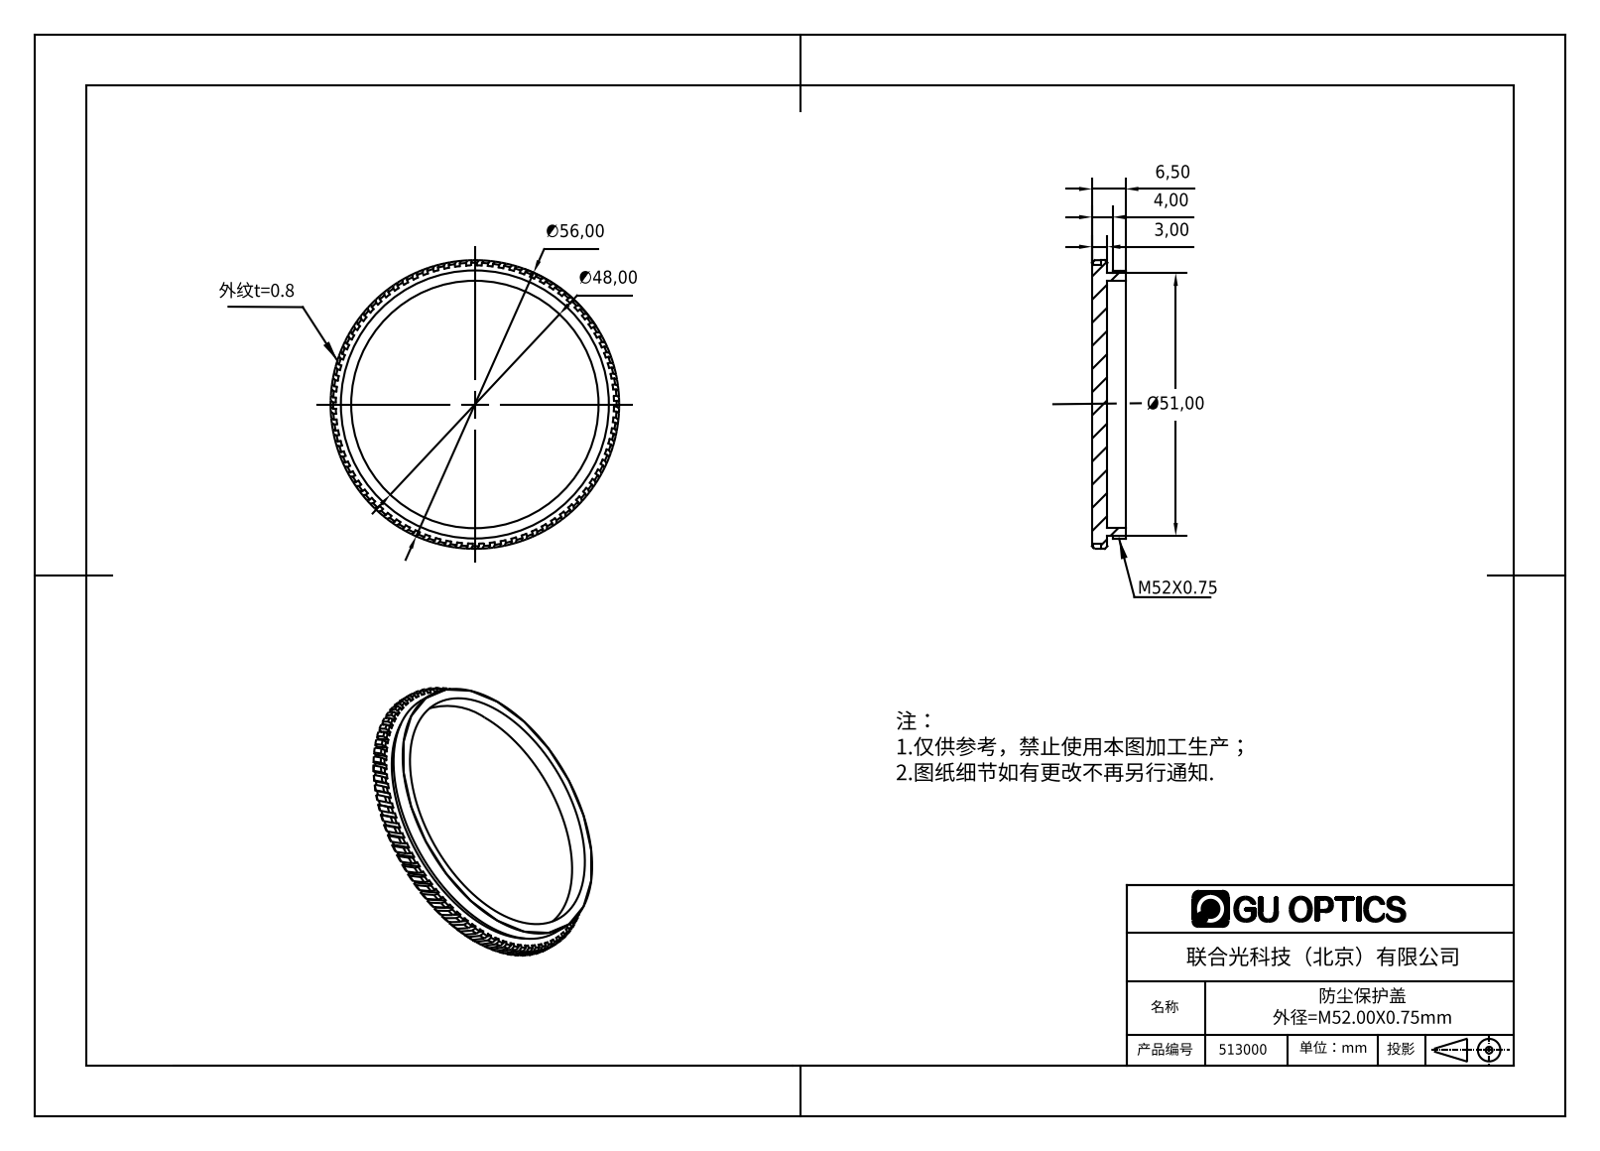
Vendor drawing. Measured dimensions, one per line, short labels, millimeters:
name: 513000
written by: SolidWorks 2016 (AUTOMOTIVE_DESIGN)
unit: mm
bodies: 1 solid, 574 faces (165 planar, 247 cylindrical, 162 other)
size: 56 × 56 × 6.5
volume: 8 155 mm³; area: 7 024 mm²
holes: 1× ⌀48
bosses: 1× ⌀56, 1× ⌀54, 1× ⌀52, 1× ⌀51
face distances: 3, 3.5, 6.5, 0.8, 2.5, 1, 4, 0.81
